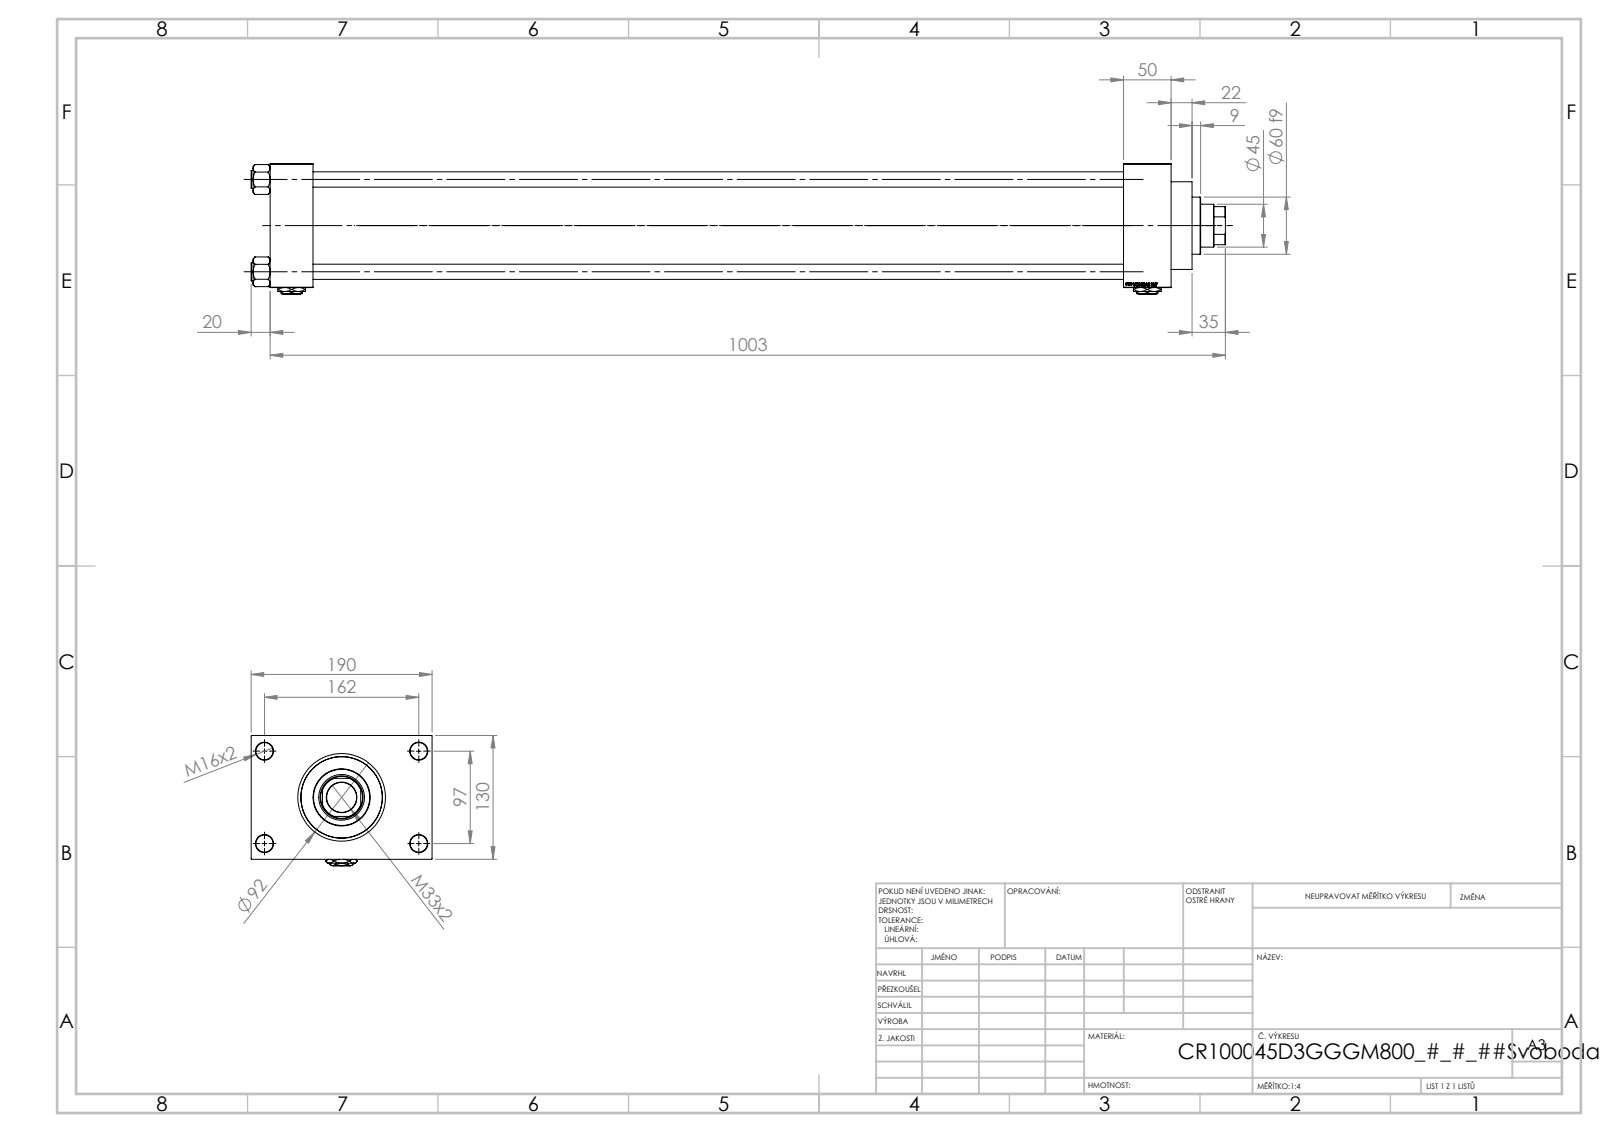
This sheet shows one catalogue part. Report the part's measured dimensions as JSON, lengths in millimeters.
{"part_name": "V215_VC_A; V215CR_D_TYCINKA; Zatka_pro_OIL_PORT; V215CR_VCP_D (+2 more)", "step_written_by": "SolidWorks 2019 (CONFIG_CONTROL_DESIGN)", "units": "millimeters", "bodies": {"solids": 13, "faces": 1253, "planar": 593, "cylindrical": 100, "other": 560}, "overall_size": [1023, 190, 137], "volume_mm3": 5218000, "surface_area_mm2": 1131000, "round_holes": [[16, 4], [18, 4], [7, 2], [26.44, 2], [35, 2], [31.5, 1], [45, 1], [48, 1], [76, 1], [85.5, 1], [100, 1]], "round_bosses_or_shafts": [[19, 4], [106, 1], [92, 1], [60, 1]], "partial_cylinders_radius": [[22, 1]], "face_to_face_distances": [130, 45, 896, 851, 946, 901, 50, 30, 160, 190], "hole_center_spacings": [32.55, 68.52, 94.41, 96.9, 102.27, 129.45, 161.73, 97]}
